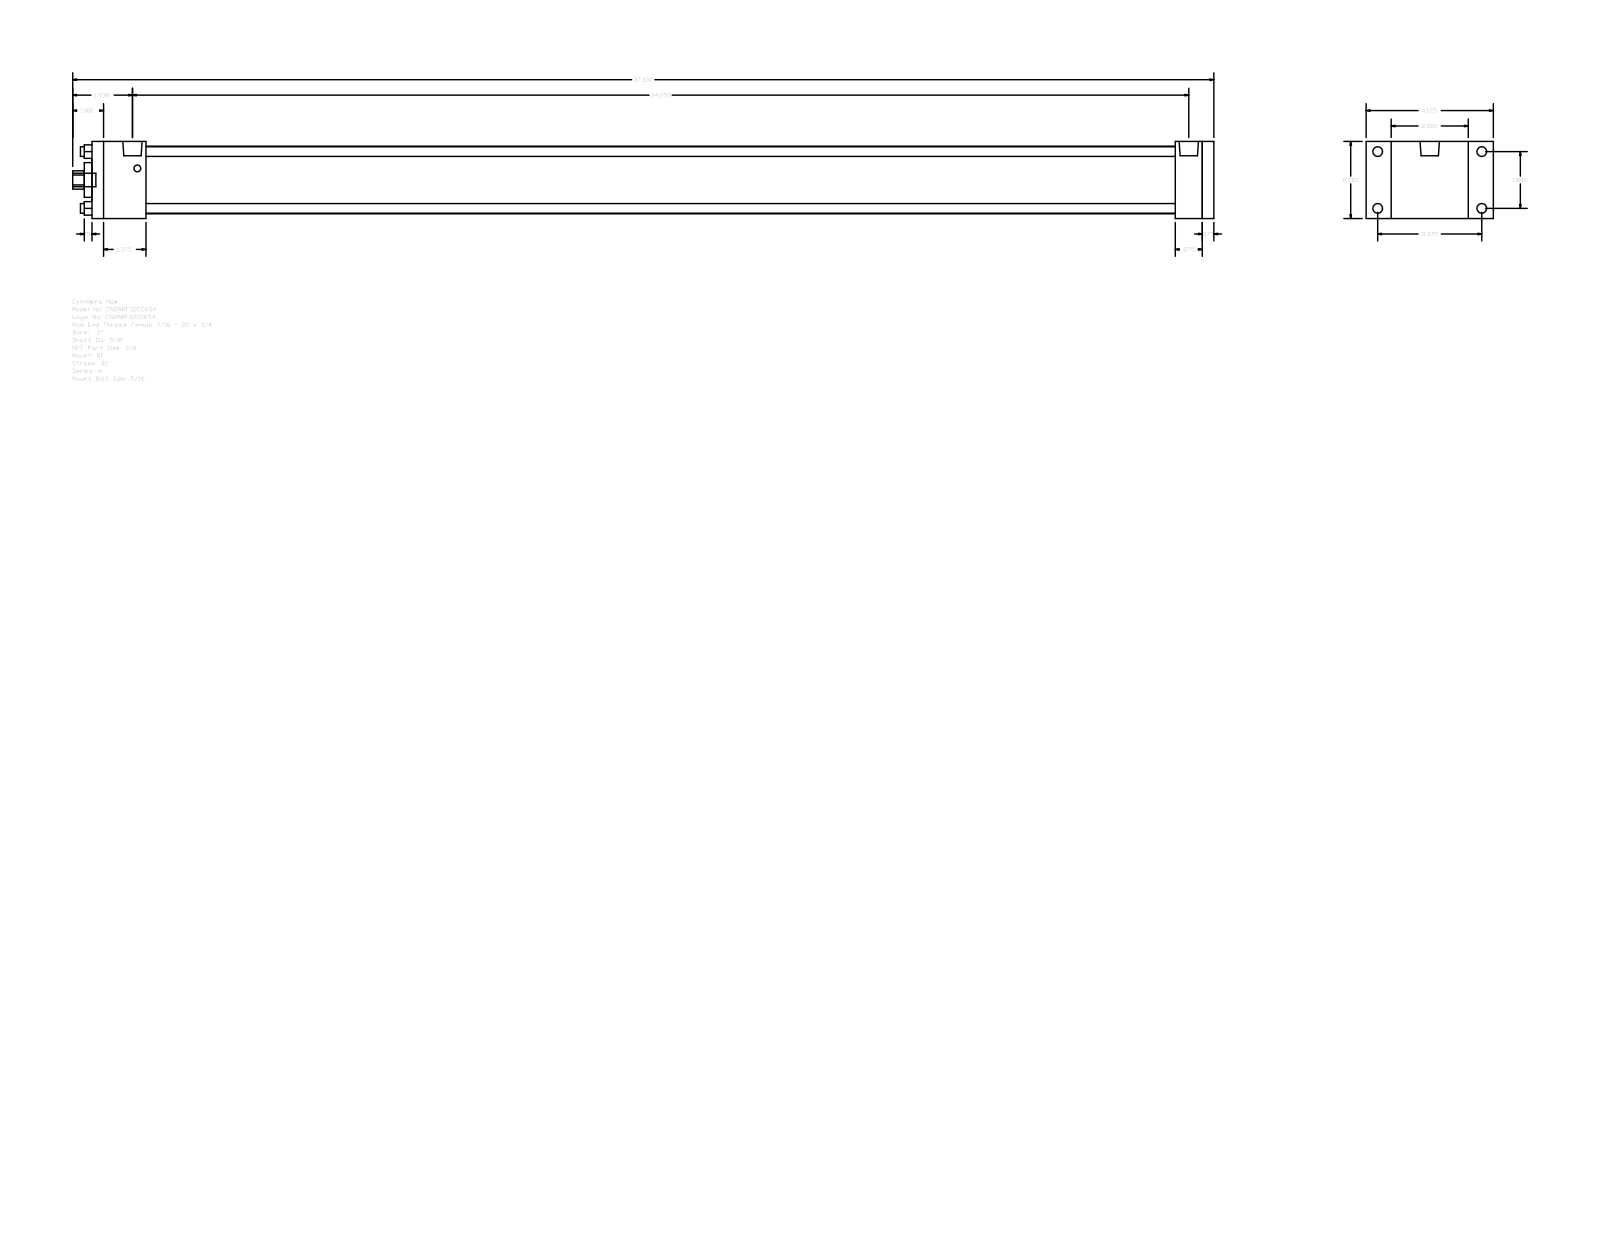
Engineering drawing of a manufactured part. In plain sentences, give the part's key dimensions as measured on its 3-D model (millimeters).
The part is named "A_RF__0200_0.625". Its 3-D file was written by "GSSL Pune (CONFIG_CONTROL_DESIGN)". It is 0 solids with 92 faces: 64 planar, 28 cylindrical and 0 other. Overall it measures 939.8 by 104.78 by 63.5 millimeters. Round holes: 4 of diameter 7.94, 1 of diameter 15.88, 1 of diameter 28.57, 1 of diameter 55.63. Round bosses or shafts: 4 of diameter 7.94, 4 of diameter 5.56, 2 of diameter 15.93, 1 of diameter 11.11. Partial cylindrical surfaces (rounded edges, fillets, slot ends): 1 of radius 7.54. The main face-to-face distances are 63.5, 923.92, 9.53, 914.39, 44.45, 869.94, 879.47, 892.17, 847.72, 22.22. The hole center spacings are 33.05, 46.74, 66.1.
